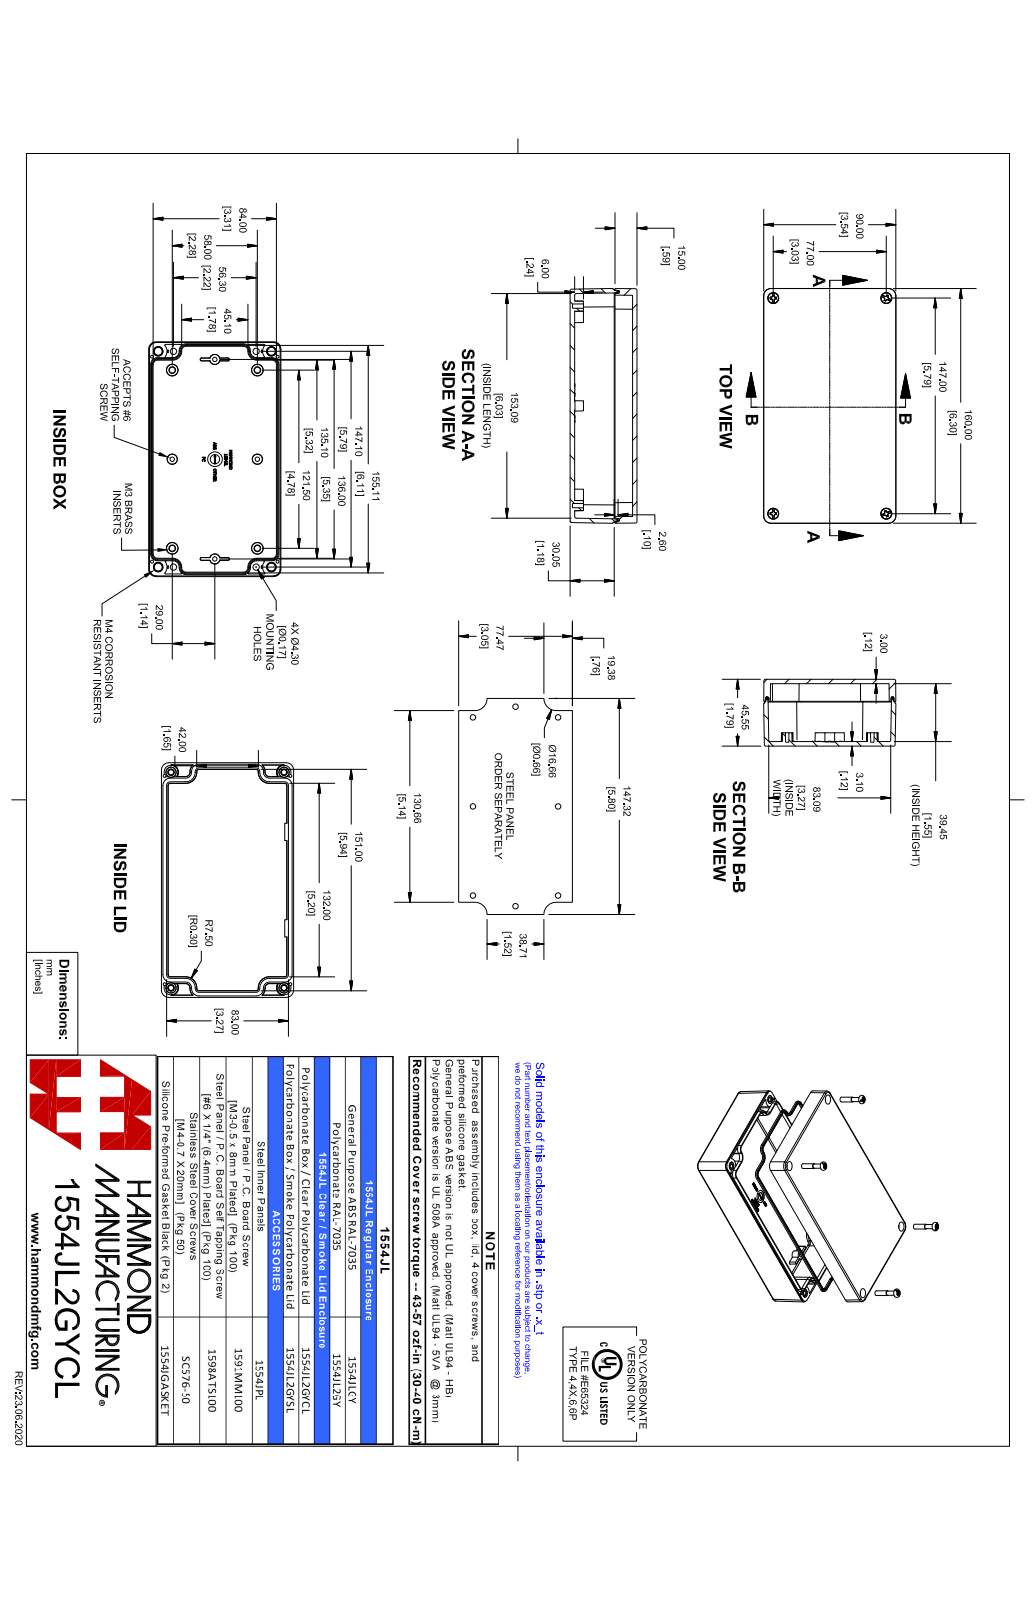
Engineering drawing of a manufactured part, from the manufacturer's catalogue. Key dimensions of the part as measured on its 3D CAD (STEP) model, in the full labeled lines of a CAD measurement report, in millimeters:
Part name (STEP PRODUCT): 1554JL2GYCL
STEP written by: SolidWorks 2021 (AUTOMOTIVE_DESIGN)
Units: millimetres
Bodies: 15 solids, 1434 faces (366 planar, 321 cylindrical, 747 other)
Overall size (bounding box): 160.1 × 90.1 × 45.5
Volume: 165 200 mm³ · Surface area: 117 500 mm²
Round holes (diameter × count): ⌀2 ×4, ⌀2.5 ×4, ⌀3.3 ×4, ⌀3.5 ×4, ⌀4.6 ×4, ⌀7 ×4
Round bosses / shafts (diameter × count): ⌀6.4 ×4, ⌀5.5 ×4, ⌀5.3 ×4, ⌀4.8 ×4, ⌀3.9 ×4, ⌀3.9 ×4, ⌀3.8 ×4, ⌀3.4 ×4
Partial cylindrical surfaces — rounded edges, fillets, slot ends (radius × count): R1 ×18, R0.5 ×16, R5 ×8, R0.8 ×4, R3 ×4, R4.7 ×4
Main face-to-face distances: 45.5, 3, 42.5, 3.1, 39.4, 42.4, 3, 4.5, 1.5, 12
Hole centre spacings: 5, 15.9, 17.2, 68.7, 72.6, 81.4, 132.5, 134.6
